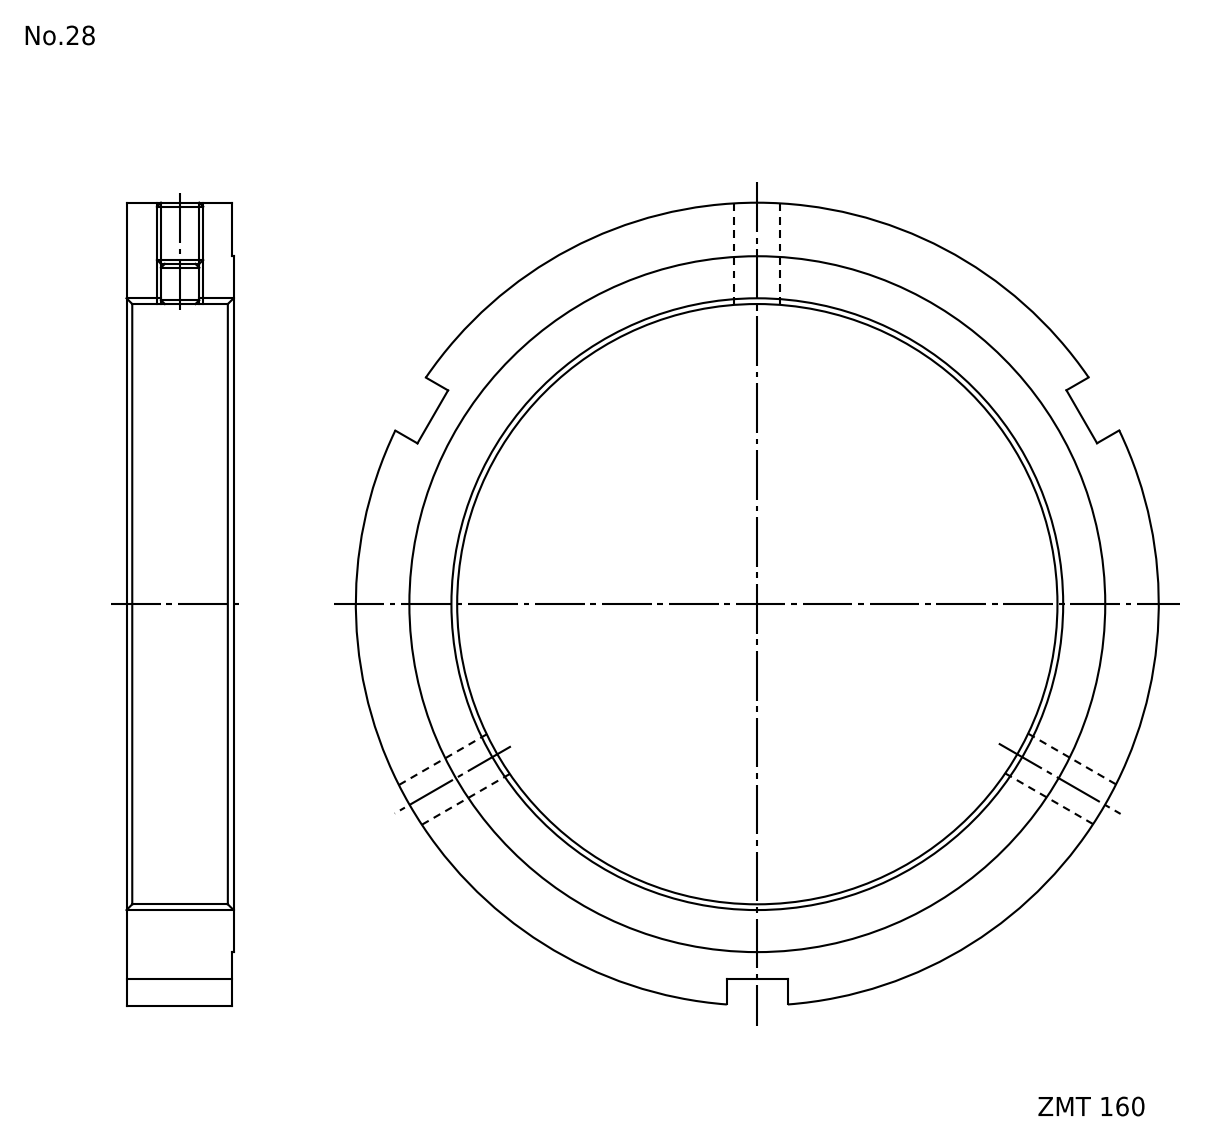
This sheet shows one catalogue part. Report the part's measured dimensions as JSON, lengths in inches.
{"part_name": "FKD ZMT160", "step_written_by": "Autodesk Inventor 2011 (AUTOMOTIVE_DESIGN)", "units": "inches", "bodies": {"solids": 1, "faces": 20, "planar": 12, "cylindrical": 8, "other": 0}, "overall_size": [8.268, 8.256, 1.102], "volume_in3": 23.64, "surface_area_in2": 99.05, "round_holes": [[0.398, 3], [6.299, 1]], "round_bosses_or_shafts": [[8.268, 1], [7.165, 1]], "face_to_face_distances": [1.083, 0.02, 1.102, 0.63]}
